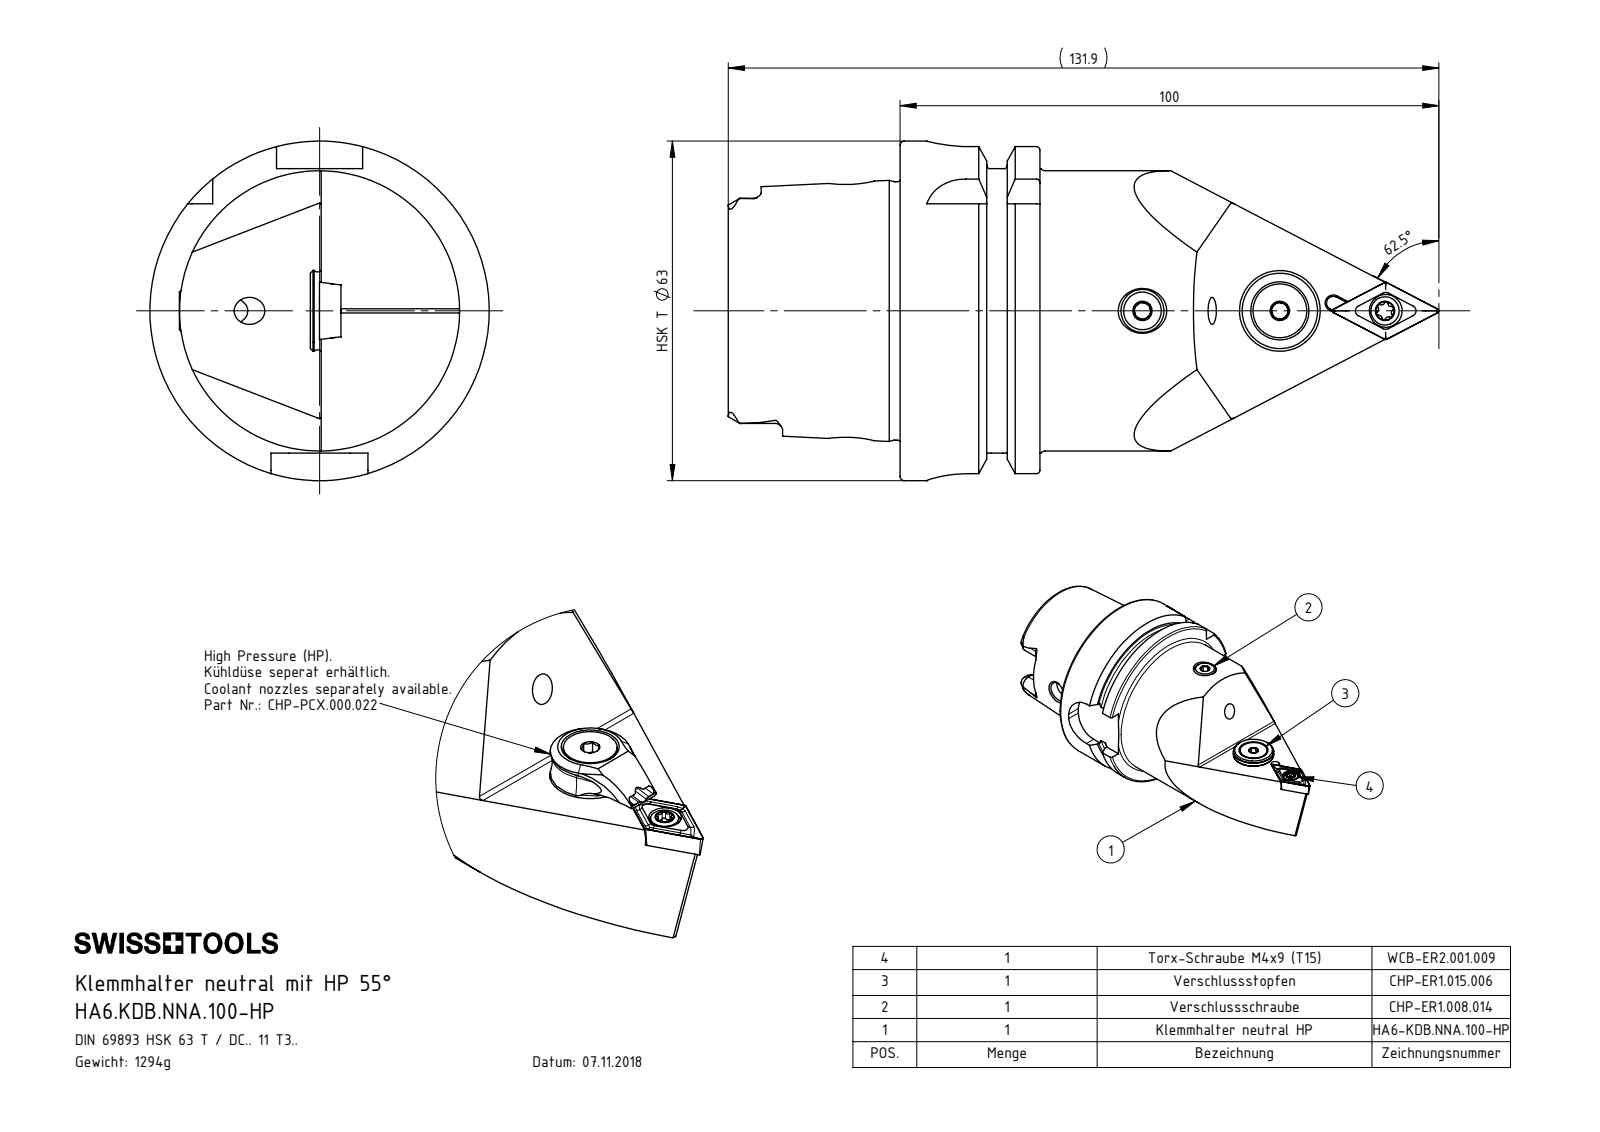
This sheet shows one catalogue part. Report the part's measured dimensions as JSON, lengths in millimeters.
{"part_name": "DCMT11T304; WCB-ER2.001.009_A; CHP-ER1.015.006; ISO 8752 2x8 (+6 more)", "step_written_by": "SolidWorks 2017 (CONFIG_CONTROL_DESIGN)", "units": "millimeters", "bodies": {"solids": 9, "faces": 314, "planar": 116, "cylindrical": 74, "other": 124}, "overall_size": [131.91, 63, 63], "volume_mm3": 165118, "surface_area_mm2": 34032, "round_holes": [[5, 3], [4.2, 2], [1.2, 1], [2, 1], [2.5, 1], [3, 1], [3.3, 1], [4.4, 1], [5.2, 1], [6.1, 1], [7, 1], [7.5, 1]], "round_bosses_or_shafts": [[63, 1], [54.95, 1], [52, 1], [47.94, 1], [15, 1], [13.4, 1], [10, 1], [8, 1]], "partial_cylinders_radius": [[0.34, 6], [0.59, 6], [1.4, 6], [2.88, 4], [8, 4], [0.8, 1], [1.25, 1]], "face_to_face_distances": [25.95, 16, 9.95, 31.9, 41.85, 57.85, 52.8, 21.8, 11.85, 4.5], "hole_center_spacings": [4.5, 16.27, 16.4, 19.52, 19.65, 25.5, 29.14, 38]}
